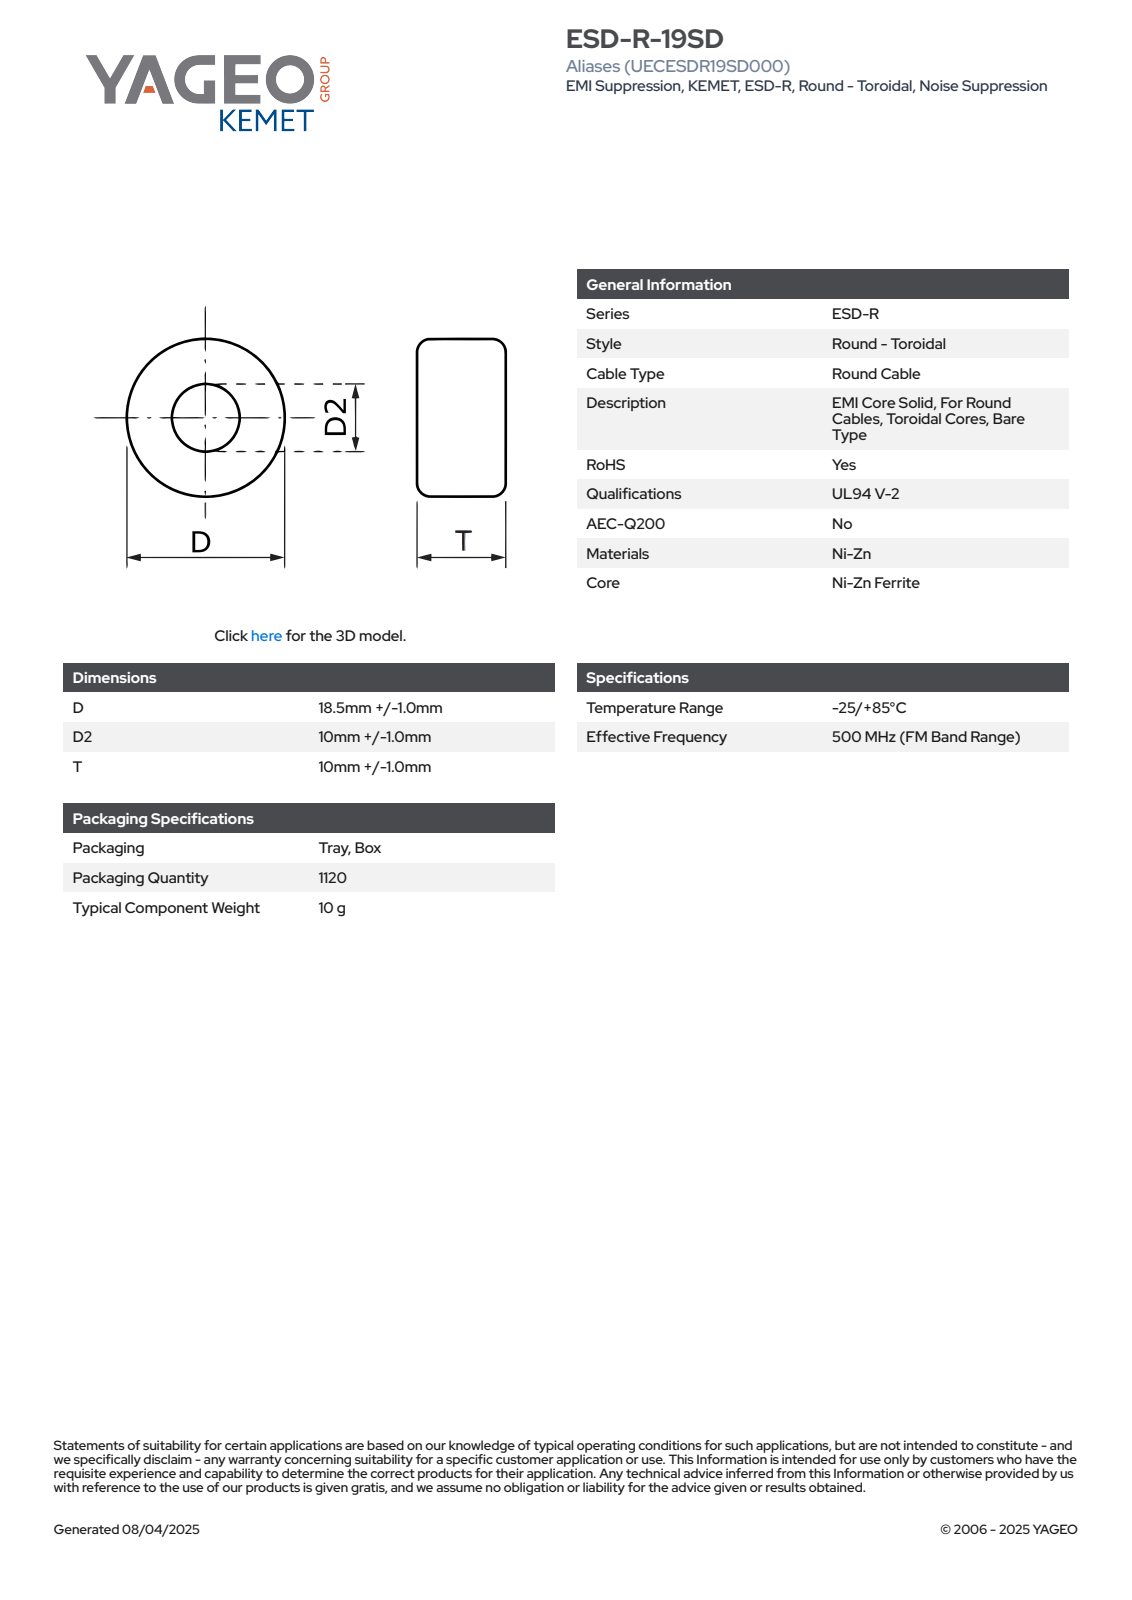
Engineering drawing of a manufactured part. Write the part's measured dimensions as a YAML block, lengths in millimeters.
part_name: "EC_KBC_D19.5D210T11"
step_written_by: "SolidWorks 2021 (AUTOMOTIVE_DESIGN)"
units: millimeters
bodies: {solids: 1, faces: 66, planar: 24, cylindrical: 7, other: 35}
overall_size: [19.51, 19.5, 11]
volume: 2412
surface_area: 1431
round_holes:
  - {diameter: 10, count: 1}
round_bosses_or_shafts:
  - {diameter: 19.5, count: 1}
partial_cylinders:
  - {radius: 9.76, count: 1}
face_to_face_distances: [11, 4.65, 6.35, 1.7, 0.32, 4.97, 6.03, 1.38, 1.06, 5.71]
